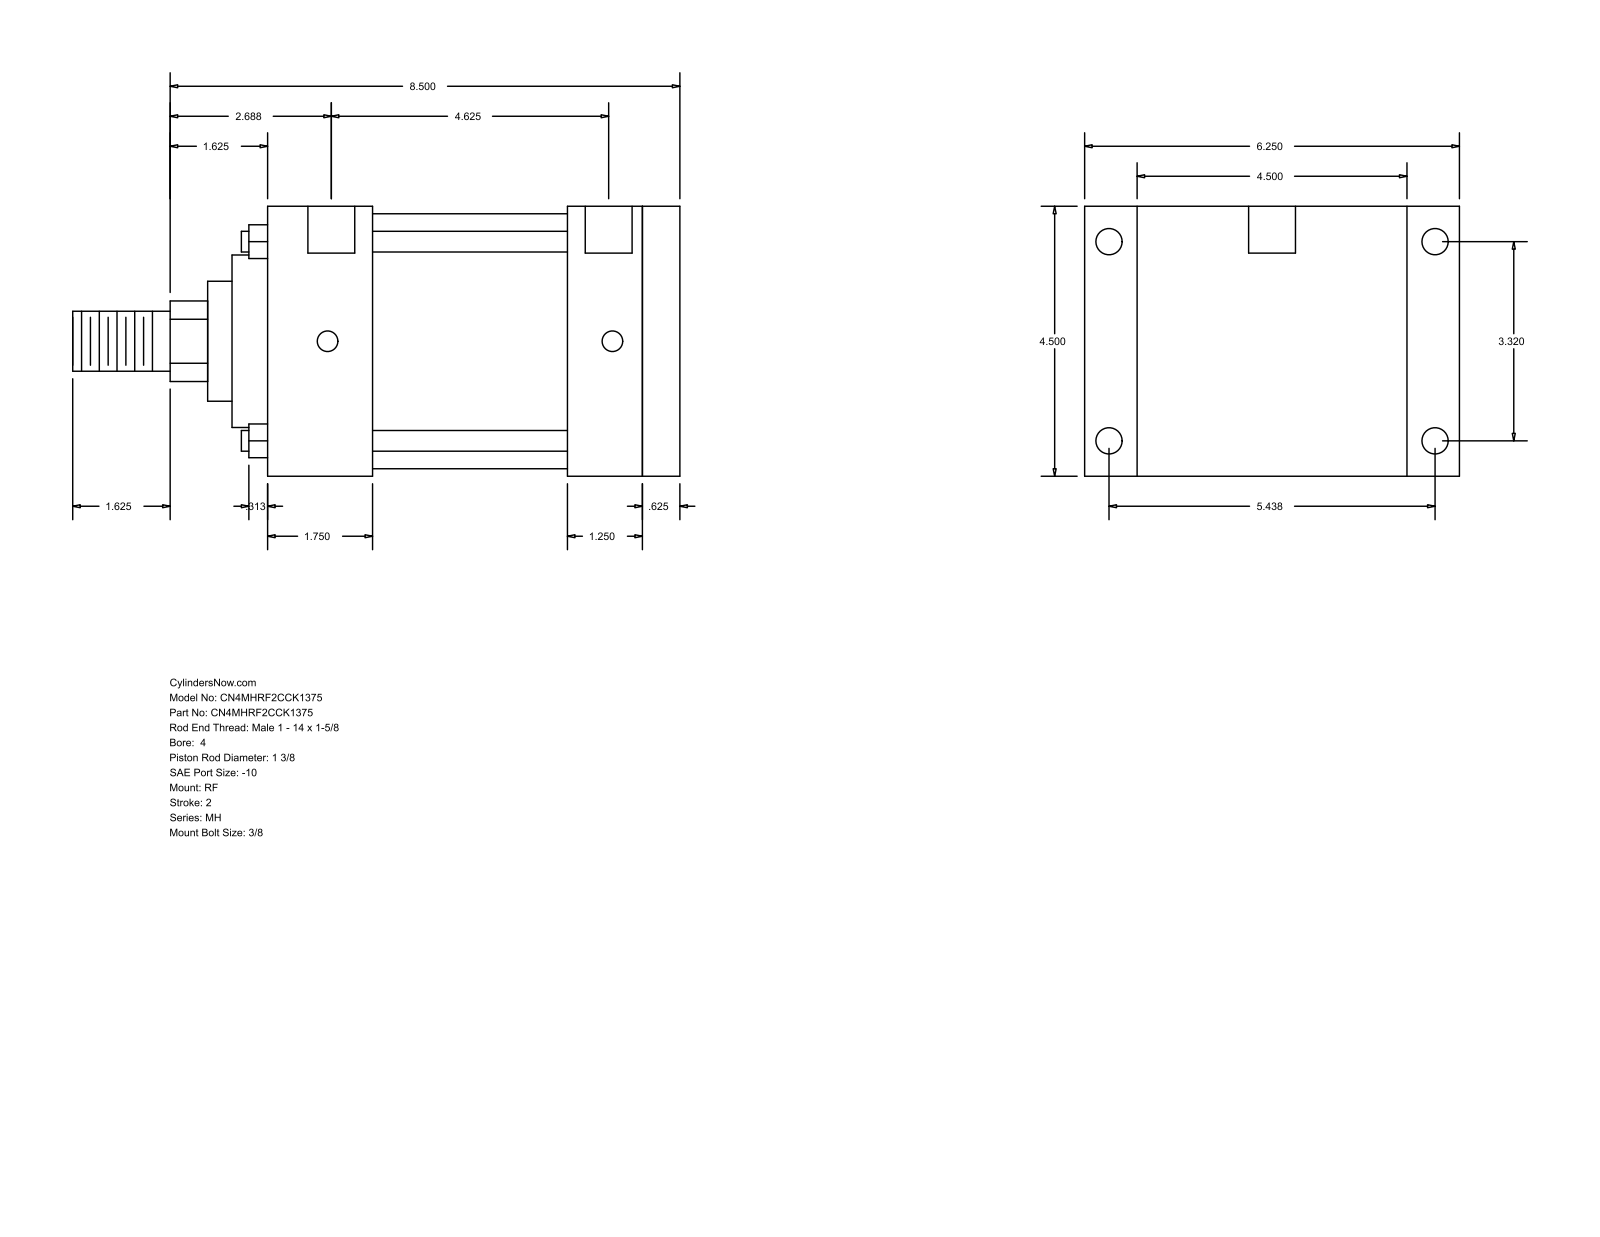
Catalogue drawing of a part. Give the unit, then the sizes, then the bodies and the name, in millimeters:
Units: millimetres
Overall size (bounding box): 257.18 × 158.75 × 114.3
Round holes (diameter × count): ⌀8.73 ×4, ⌀11.13 ×4, ⌀19.84 ×2
Round bosses / shafts (diameter × count): ⌀8.76 ×4, ⌀107.95 ×1, ⌀73.03 ×1, ⌀50.8 ×1, ⌀34.92 ×1, ⌀25.4 ×1
Partial cylindrical surfaces — rounded edges, fillets, slot ends (radius × count): R17.06 ×1
Main face-to-face distances: 114.3, 174.63, 158.76, 15.87, 44.45, 114.31, 130.18, 127.01, 82.56, 31.75
Hole centre spacings: 84.32, 120.65, 138.12, 161.82, 1.58, 1.59, 117.48, 119.06
Bodies: 0 solids, 94 faces (65 planar, 29 cylindrical, 0 other)
Part name (STEP PRODUCT): MH_RF__0400_1.375
STEP written by: GSSL Pune (CONFIG_CONTROL_DESIGN)
